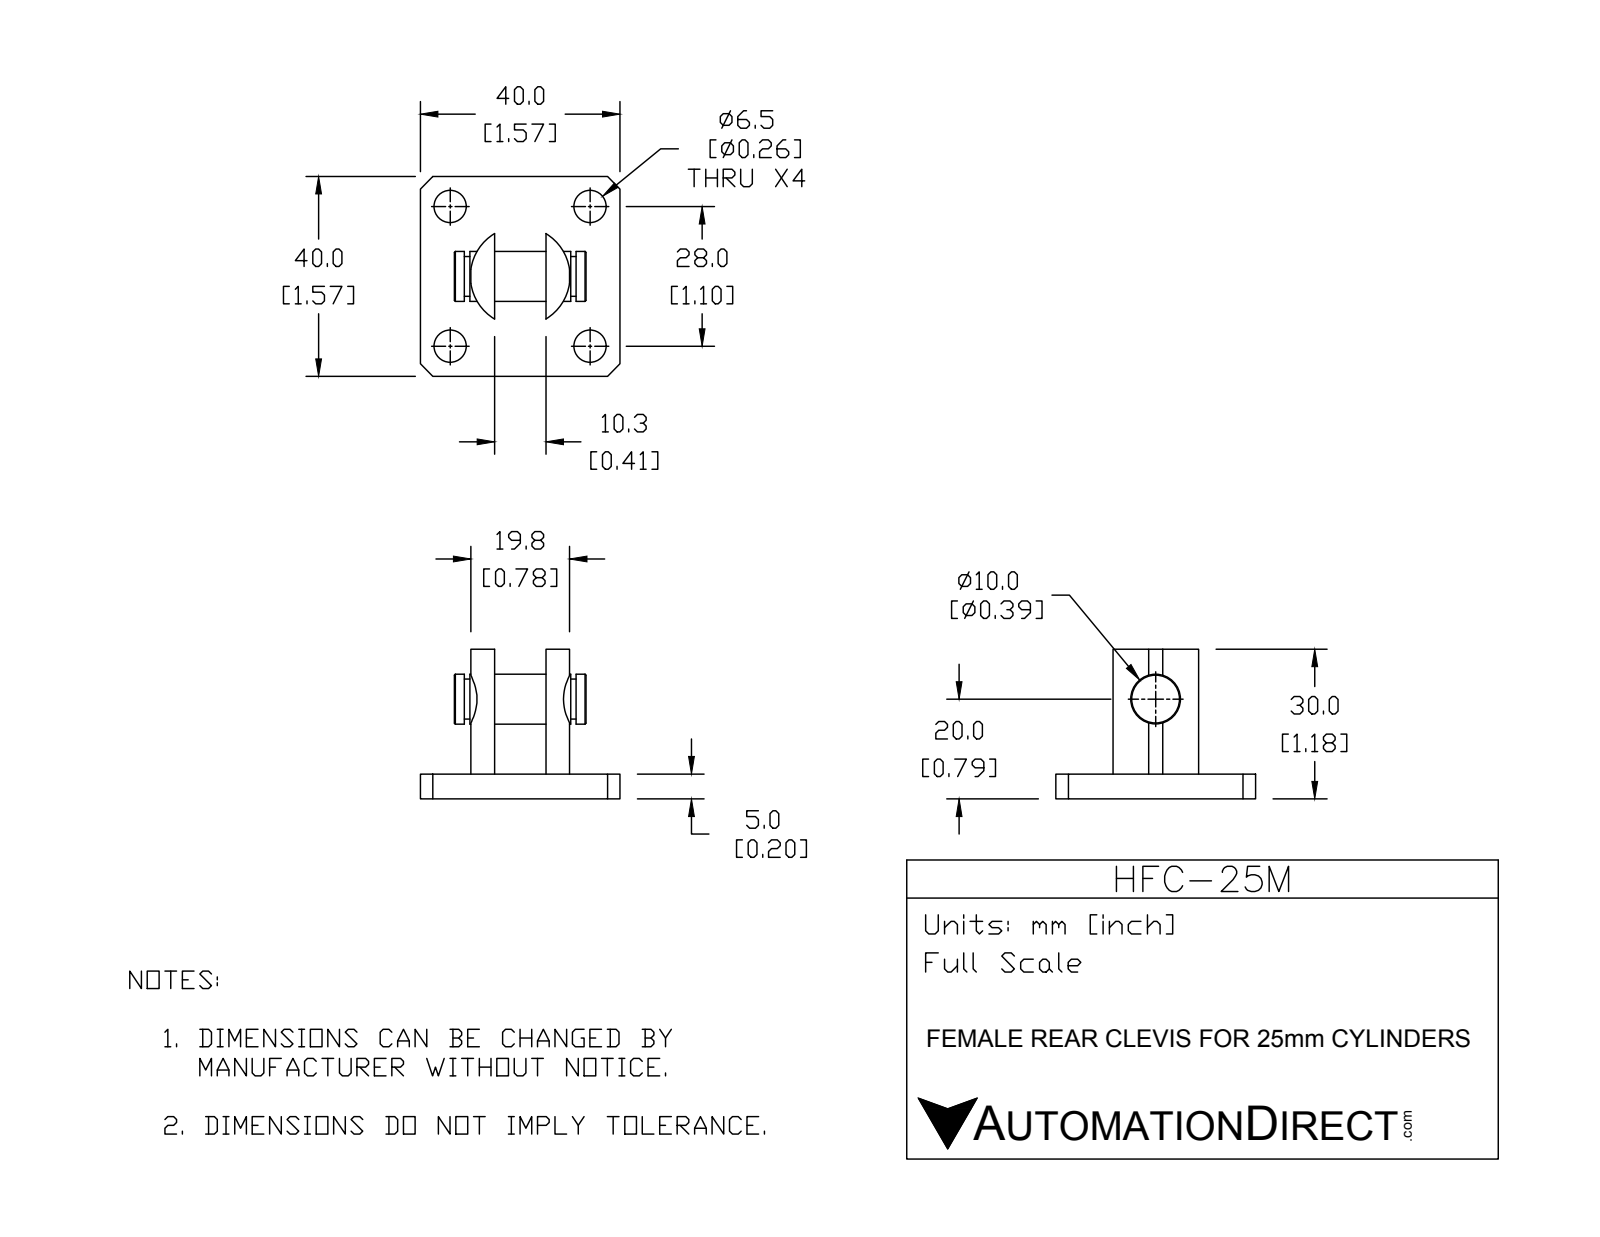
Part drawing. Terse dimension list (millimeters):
name: HFC-25M
written by: SolidWorks 2015 (CONFIG_CONTROL_DESIGN)
unit: mm
bodies: 2 solids, 54 faces (24 planar, 26 cylindrical, 4 other)
size: 40 × 40 × 30
volume: 11 509 mm³; area: 6 997 mm²
holes: 4× ⌀6.5
bosses: 1× ⌀10, 1× ⌀8
rounds: 1× R10
face distances: 5, 10.3, 40, 14.85, 25.15, 6.8, 33.2, 8.05, 18.35, 30
hole spacings: 28, 39.6
